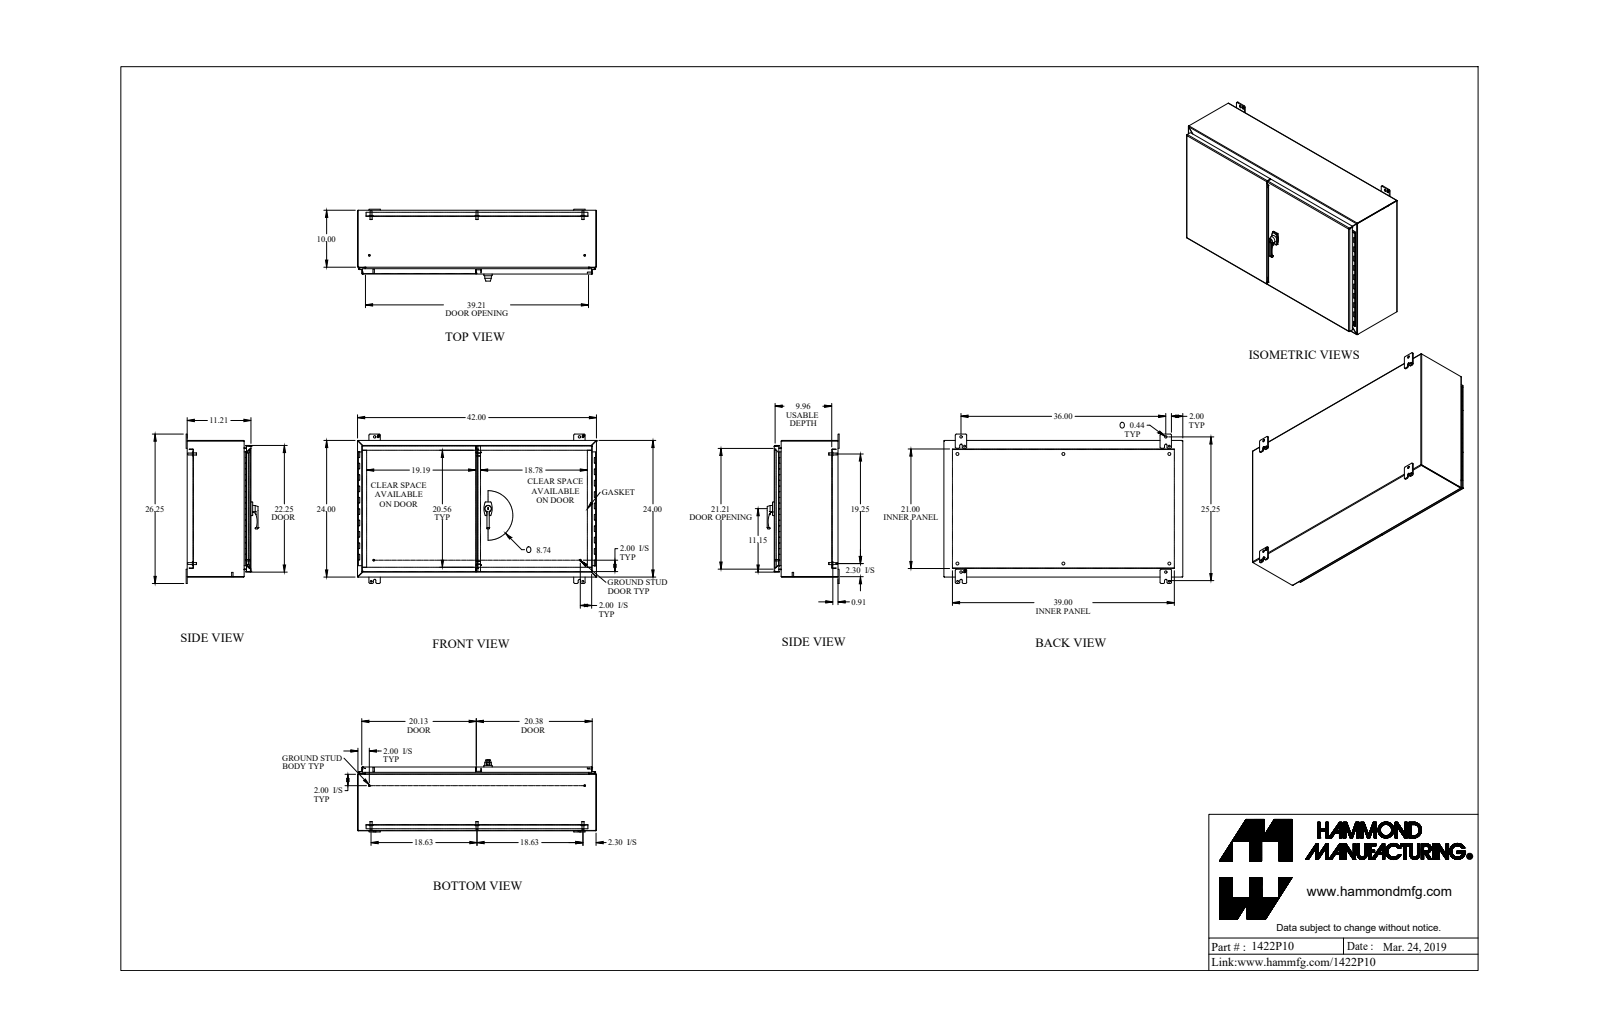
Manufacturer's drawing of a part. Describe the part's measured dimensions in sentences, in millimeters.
The part is named "1422P10". Its 3-D file was written by "SolidWorks 2019 (AUTOMOTIVE_DESIGN)". It is 0 solids with 1493 faces: 920 planar, 423 cylindrical and 150 other. Overall it measures 1066.8 by 666.8 by 321 millimeters. Round holes: 8 of diameter 7.7, 7 of diameter 7.8, 6 of diameter 11.3, 6 of diameter 12.7, 4 of diameter 5.5, 4 of diameter 8, 4 of diameter 11.1, 2 of diameter 2.8, 2 of diameter 3.2, 2 of diameter 4, 2 of diameter 4.7, 2 of diameter 4.8. Round bosses or shafts: 7 of diameter 25.4, 6 of diameter 16.5, 6 of diameter 9.5, 6 of diameter 8.4, 5 of diameter 12.7, 4 of diameter 8, 4 of diameter 7.1, 4 of diameter 6.4. Partial cylindrical surfaces (rounded edges, fillets, slot ends): 27 of radius 4.8, 18 of radius 1.2, 18 of radius 3.6, 16 of radius 0.9, 16 of radius 1.3, 16 of radius 2.7, 9 of radius 2.5, 8 of radius 1.1. The main face-to-face distances are 1.8, 280.5, 282.3, 2.4, 2.4, 23.8, 282.9, 284.7, 256.7, 254.3. The hole center spacings are 473.1, 680.3, 43, 152.4, 513.2, 986.2, 1036.9, 1037.2.
